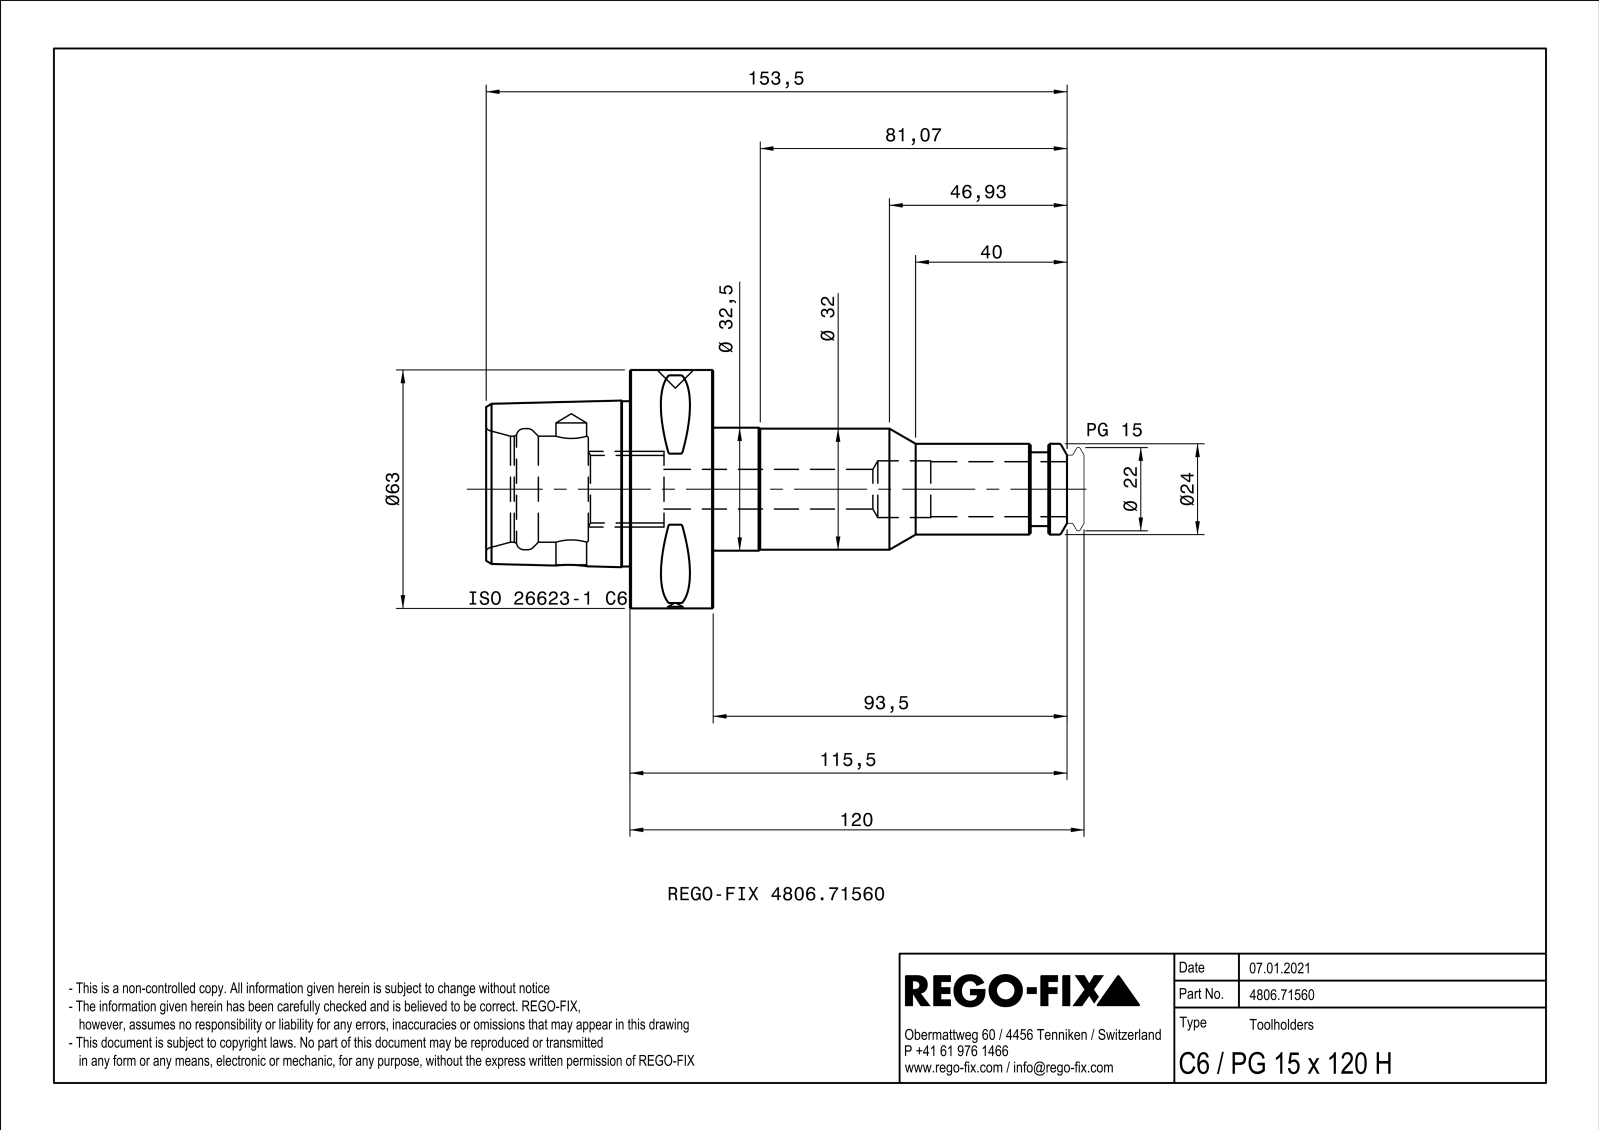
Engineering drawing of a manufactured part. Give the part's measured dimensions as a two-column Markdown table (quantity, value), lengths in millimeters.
| quantity | value |
| --- | --- |
| part name | NOCUT |
| STEP written by | SIEMENS PLM Software Solid Edge ST10 (AUTOMOTIVE_DESIGN) |
| units | millimeters |
| bodies | 1 solid, 131 faces (23 planar, 27 cylindrical, 81 other) |
| overall size | 153.5 × 63 × 63 |
| volume | 142 207 mm³ |
| surface area | 31 866 mm² |
| round holes (diameter × count) | 4 × 1, 8.1 × 1, 10.5 × 1, 15 × 1, 17.84 × 1, 28 × 1, 32 × 1 |
| round bosses / shafts (diameter × count) | 63 × 1, 32.5 × 1, 24 × 1, 19.5 × 1 |
| partial cylindrical surfaces (radius × count) | 0.5 × 8, 5 × 1 |
| main face-to-face distances | 22, 60, 38, 24.89, 33, 11, 27, 55.8, 22.1, 10.9 |
| hole center spacings | 27.5 |
